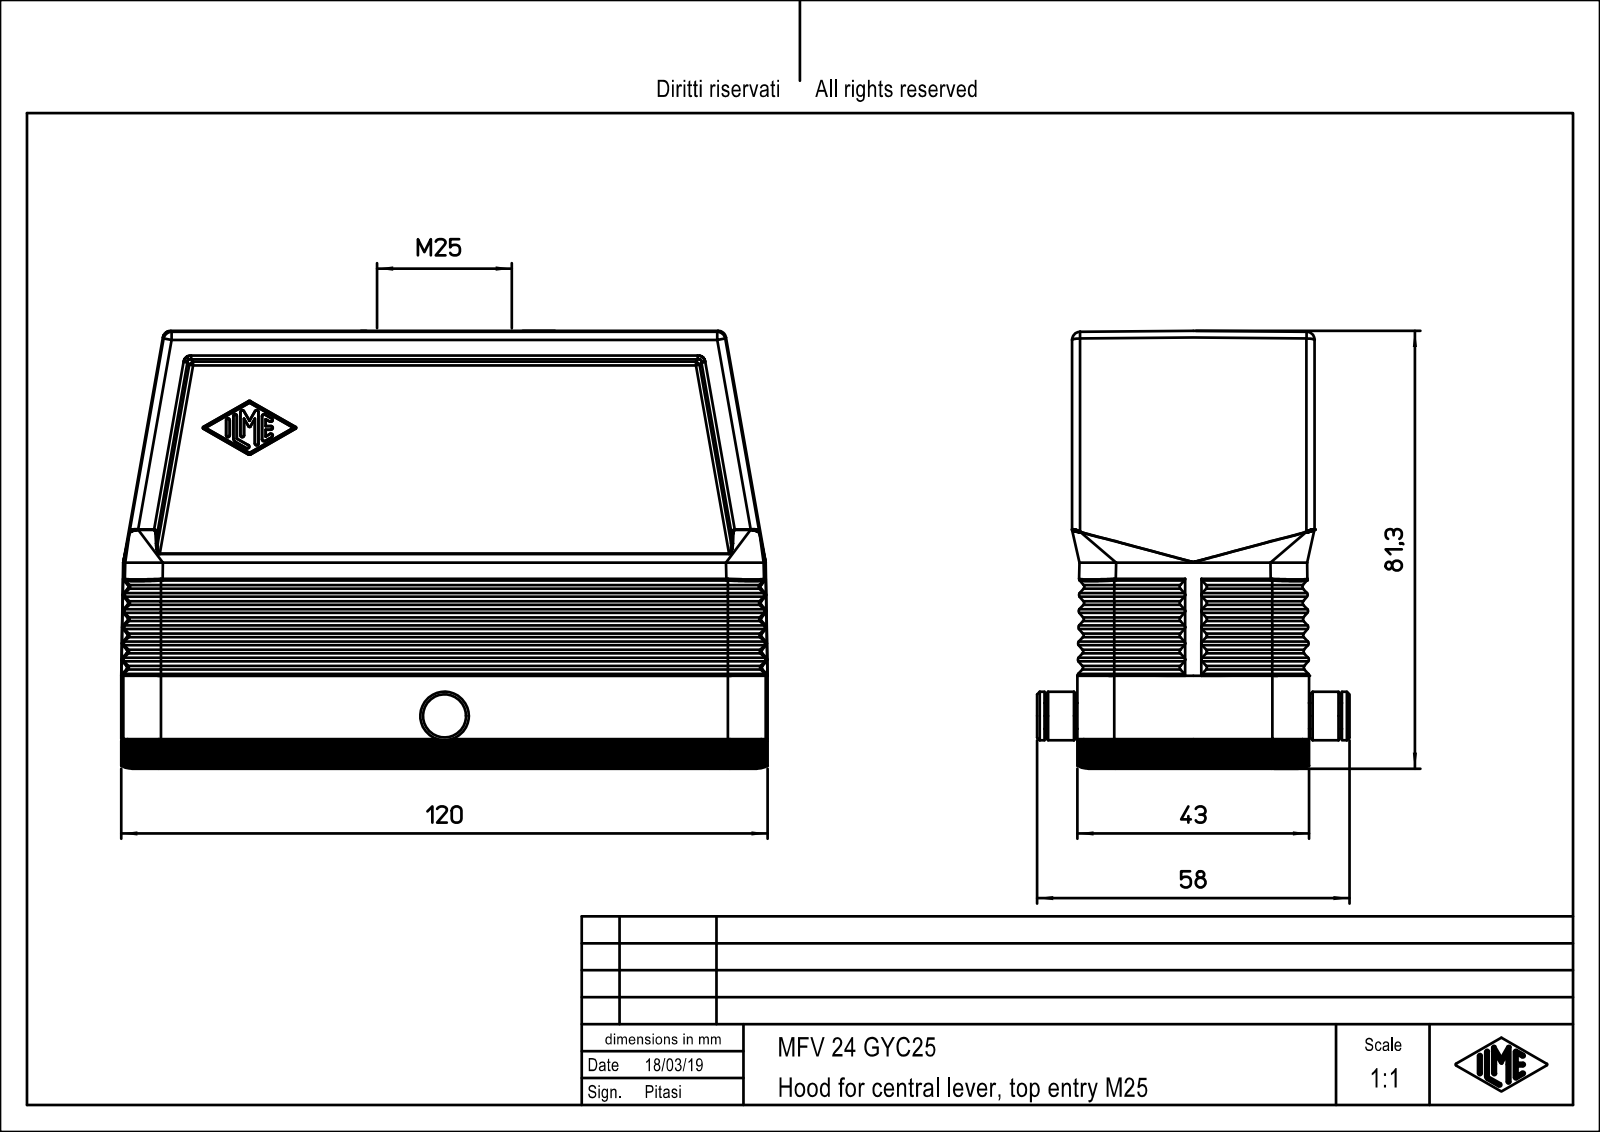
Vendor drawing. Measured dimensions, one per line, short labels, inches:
name: MFV_24_GYC25
written by: PTC Creo Elements/Direct Modeling 19.0E 27-Jun-2016 (C) Parametric Technology GmbH (AUTOMOTIVE_DESIGN)
unit: in
bodies: 1 solid, 573 faces (223 planar, 182 cylindrical, 168 other)
size: 4.724 × 3.199 × 2.283
volume: 7.697 in³; area: 91.34 in²
holes: 4× ⌀0.118, 1× ⌀0.984
bosses: 1× ⌀0.354, 1× ⌀0.189
rounds: 84× R0.02, 16× R0.039, 12× R0.276, 10× R0.059, 8× R0.118, 4× R0.138, 4× R0.157, 4× R0.165
face distances: 1.693, 0.039, 0.157, 0.079, 0.237, 1.535, 0.158, 0.315, 0.197, 1.575
hole spacings: 1.063, 2.115, 2.115, 4.094, 4.23
